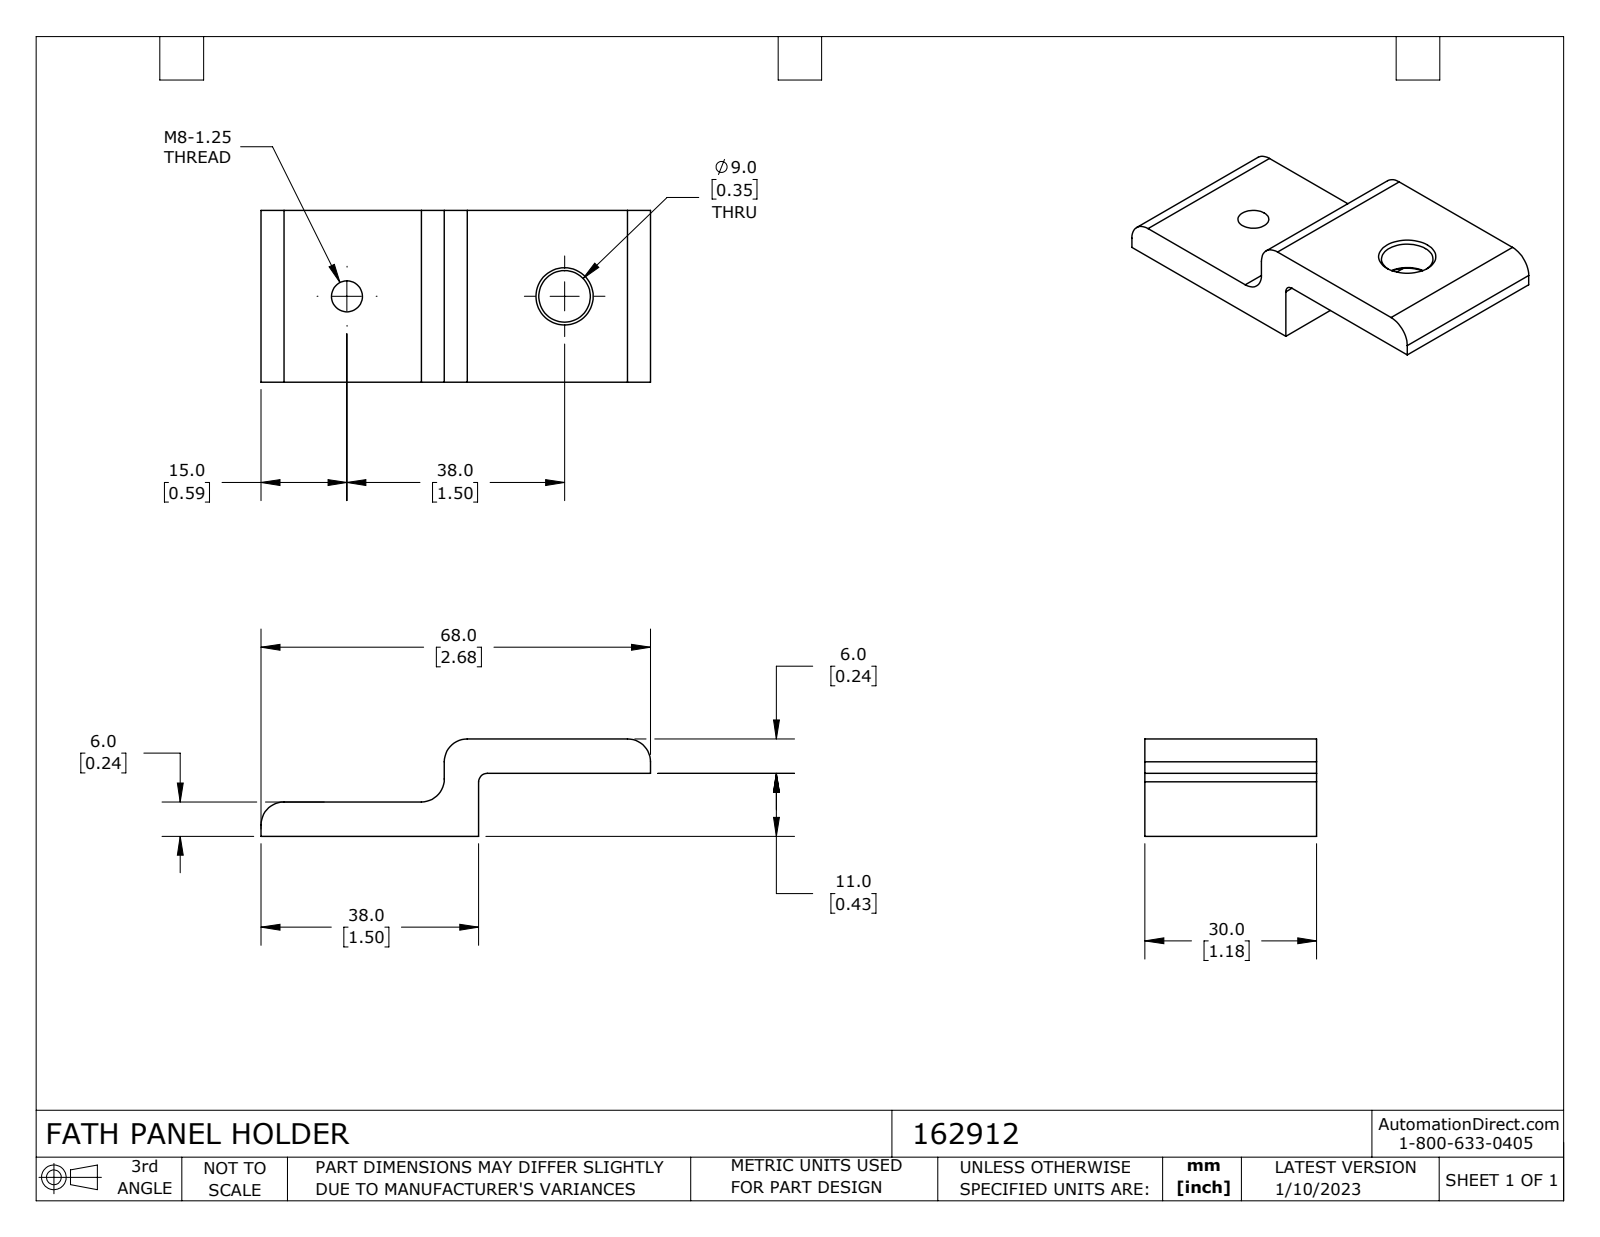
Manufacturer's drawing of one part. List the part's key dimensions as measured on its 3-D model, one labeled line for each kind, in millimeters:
Part name (STEP PRODUCT): 162912
STEP written by: SolidWorks 2021 (CONFIG_CONTROL_DESIGN)
Units: millimetres
Bodies: 1 solid, 23 faces (10 planar, 9 cylindrical, 4 other)
Overall size (bounding box): 68 × 30 × 17
Volume: 13 500 mm³ · Surface area: 5 892 mm²
Round holes (diameter × count): ⌀5.4 ×1, ⌀9 ×1
Partial cylindrical surfaces — rounded edges, fillets, slot ends (radius × count): R4 ×4, R1.5 ×1
Main face-to-face distances: 6, 11, 17, 5, 30, 38, 32, 36, 68
Hole centre spacings: 38
